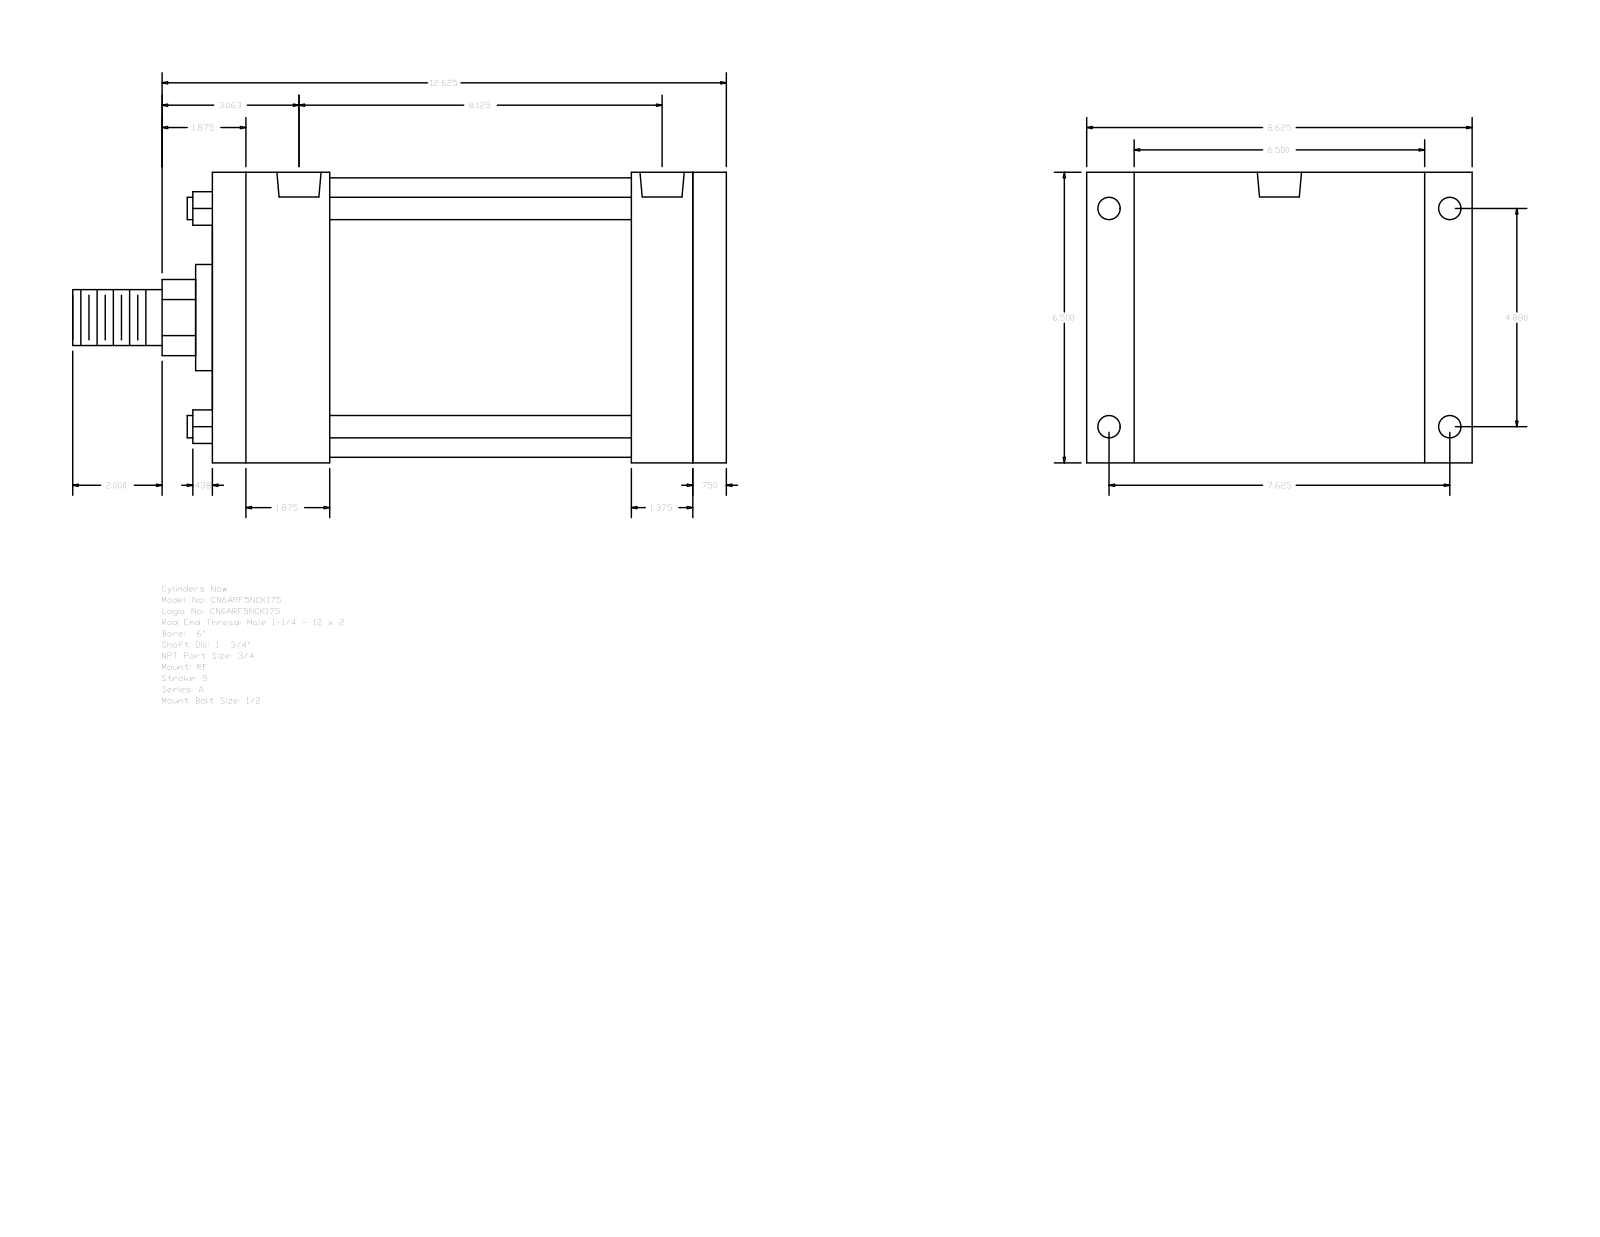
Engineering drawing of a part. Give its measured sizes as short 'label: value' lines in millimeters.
name: A_RF__0600_1.75
written by: GSSL Pune (CONFIG_CONTROL_DESIGN)
unit: mm
bodies: 0 solids, 92 faces (64 planar, 28 cylindrical, 0 other)
size: 371.48 × 219.07 × 165.1
holes: 4× ⌀12.7, 4× ⌀15.08, 2× ⌀25.12
bosses: 4× ⌀12.7, 1× ⌀158.75, 1× ⌀60.33, 1× ⌀44.45, 1× ⌀31.75
rounds: 1× R21.63
face distances: 165.1, 292.11, 273.05, 19.06, 66.68, 206.37, 225.43, 238.13, 171.45, 34.92
hole spacings: 5.56, 123.96, 193.68, 195.25, 200.81, 229.95, 206.37
